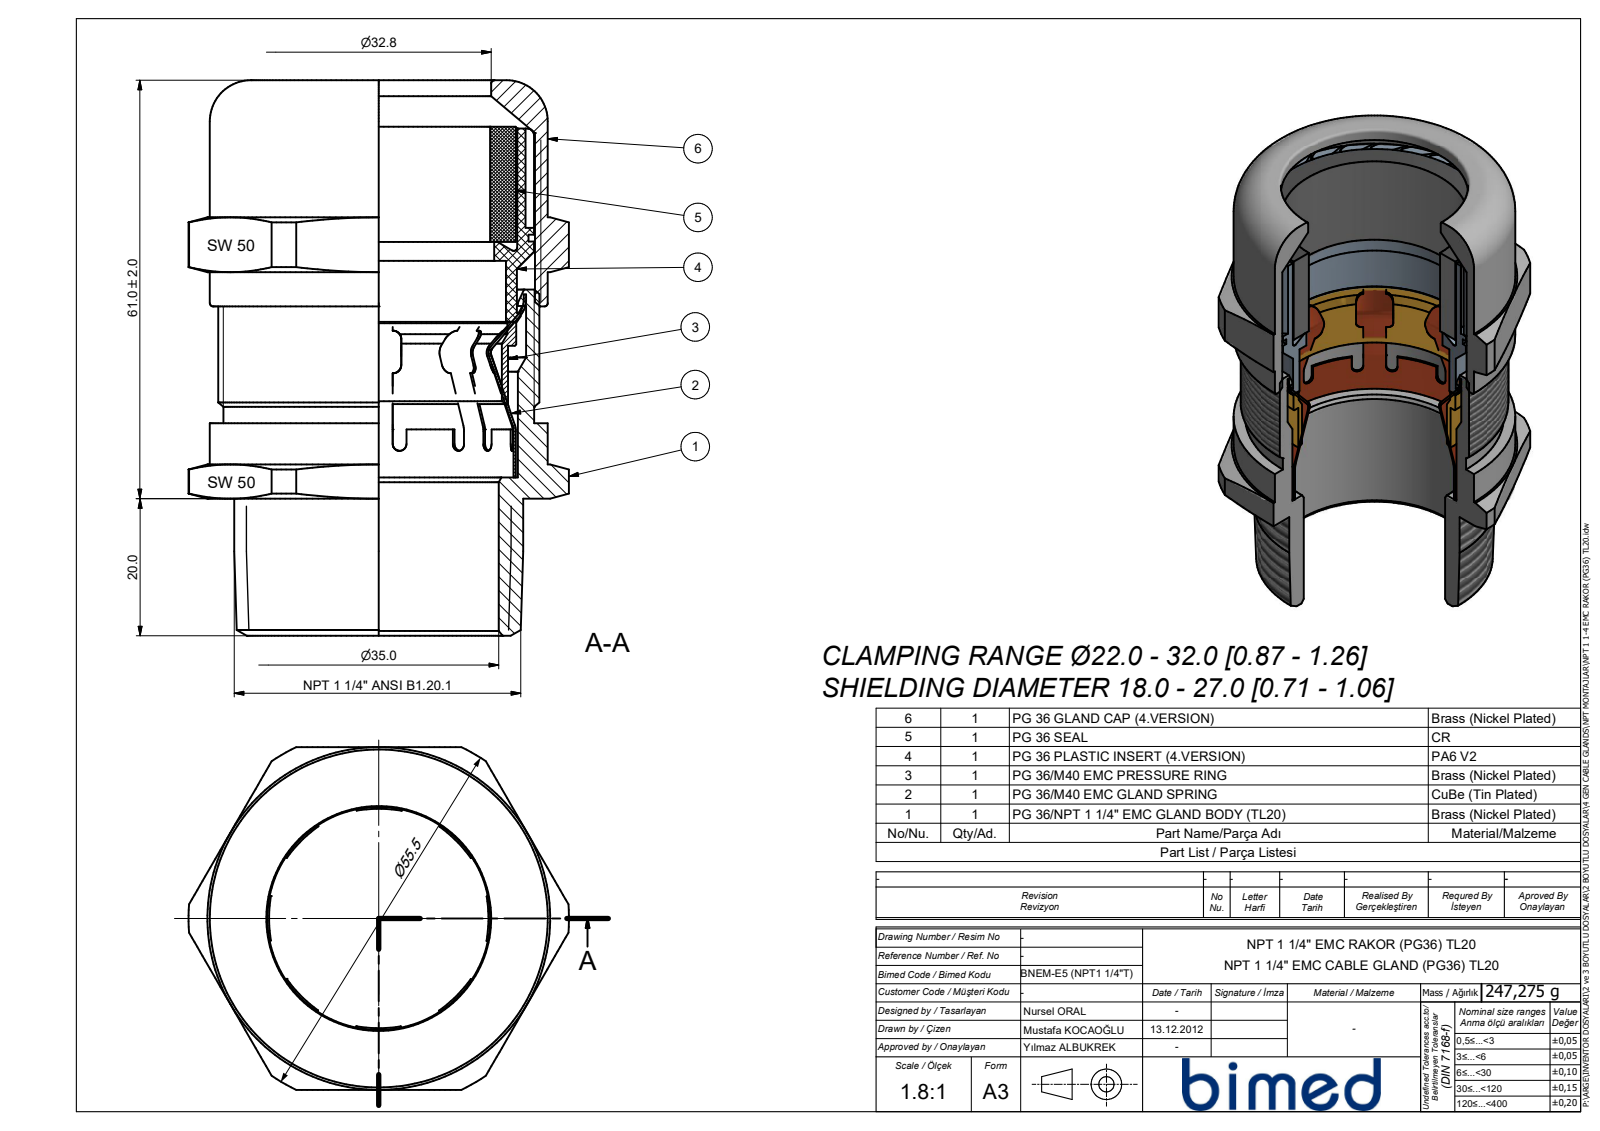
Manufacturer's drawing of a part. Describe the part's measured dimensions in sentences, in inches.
The part is named "BNEM-E5-11-4T-WCL". Its 3-D file was written by "SolidWorks 2021 (CONFIG_CONTROL_DESIGN)". It is 1 solid with 91 faces: 21 planar, 26 cylindrical and 44 other. Overall it measures 3.191 by 2.185 by 1.969 inches. Its volume is 8.689 cubic inches and its surface area 25.86 square inches. Round bosses or shafts: 1 of diameter 1.941, 1 of diameter 1.844, 1 of diameter 1.785. Partial cylindrical surfaces (rounded edges, fillets, slot ends): 1 of radius 1.093. The main face-to-face distances are 3.191, 1.969, 0.787, 2.403, 1.22, 0.433, 1.97, 1.104, 0.197, 1.891.
